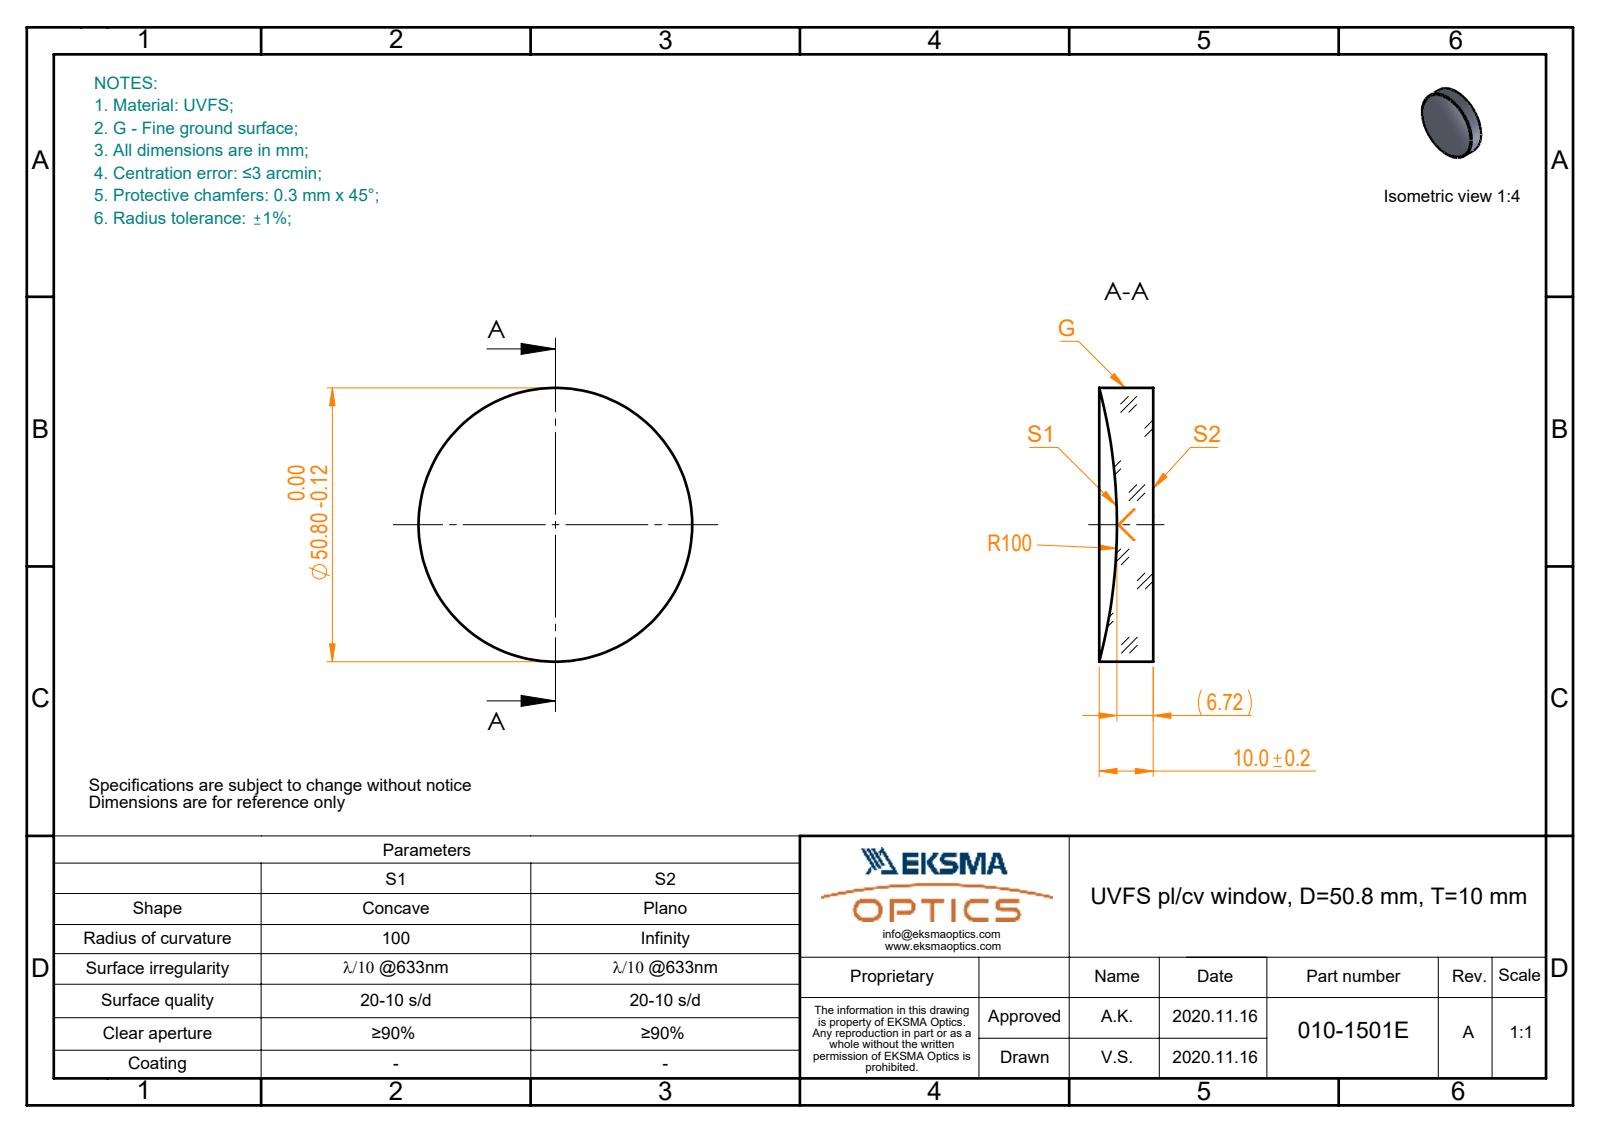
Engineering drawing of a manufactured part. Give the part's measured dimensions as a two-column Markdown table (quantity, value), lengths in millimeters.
| quantity | value |
| --- | --- |
| part name | 010-1501E_UVFS_PCV_window |
| STEP written by | SolidWorks 2019 (CONFIG_CONTROL_DESIGN) |
| units | millimeters |
| bodies | 1 solid, 5 faces (1 planar, 2 cylindrical, 2 other) |
| overall size | 50.8 × 50.8 × 10 |
| volume | 16 926 mm³ |
| surface area | 5 683 mm² |
| round bosses / shafts (diameter × count) | 50.8 × 1 |
